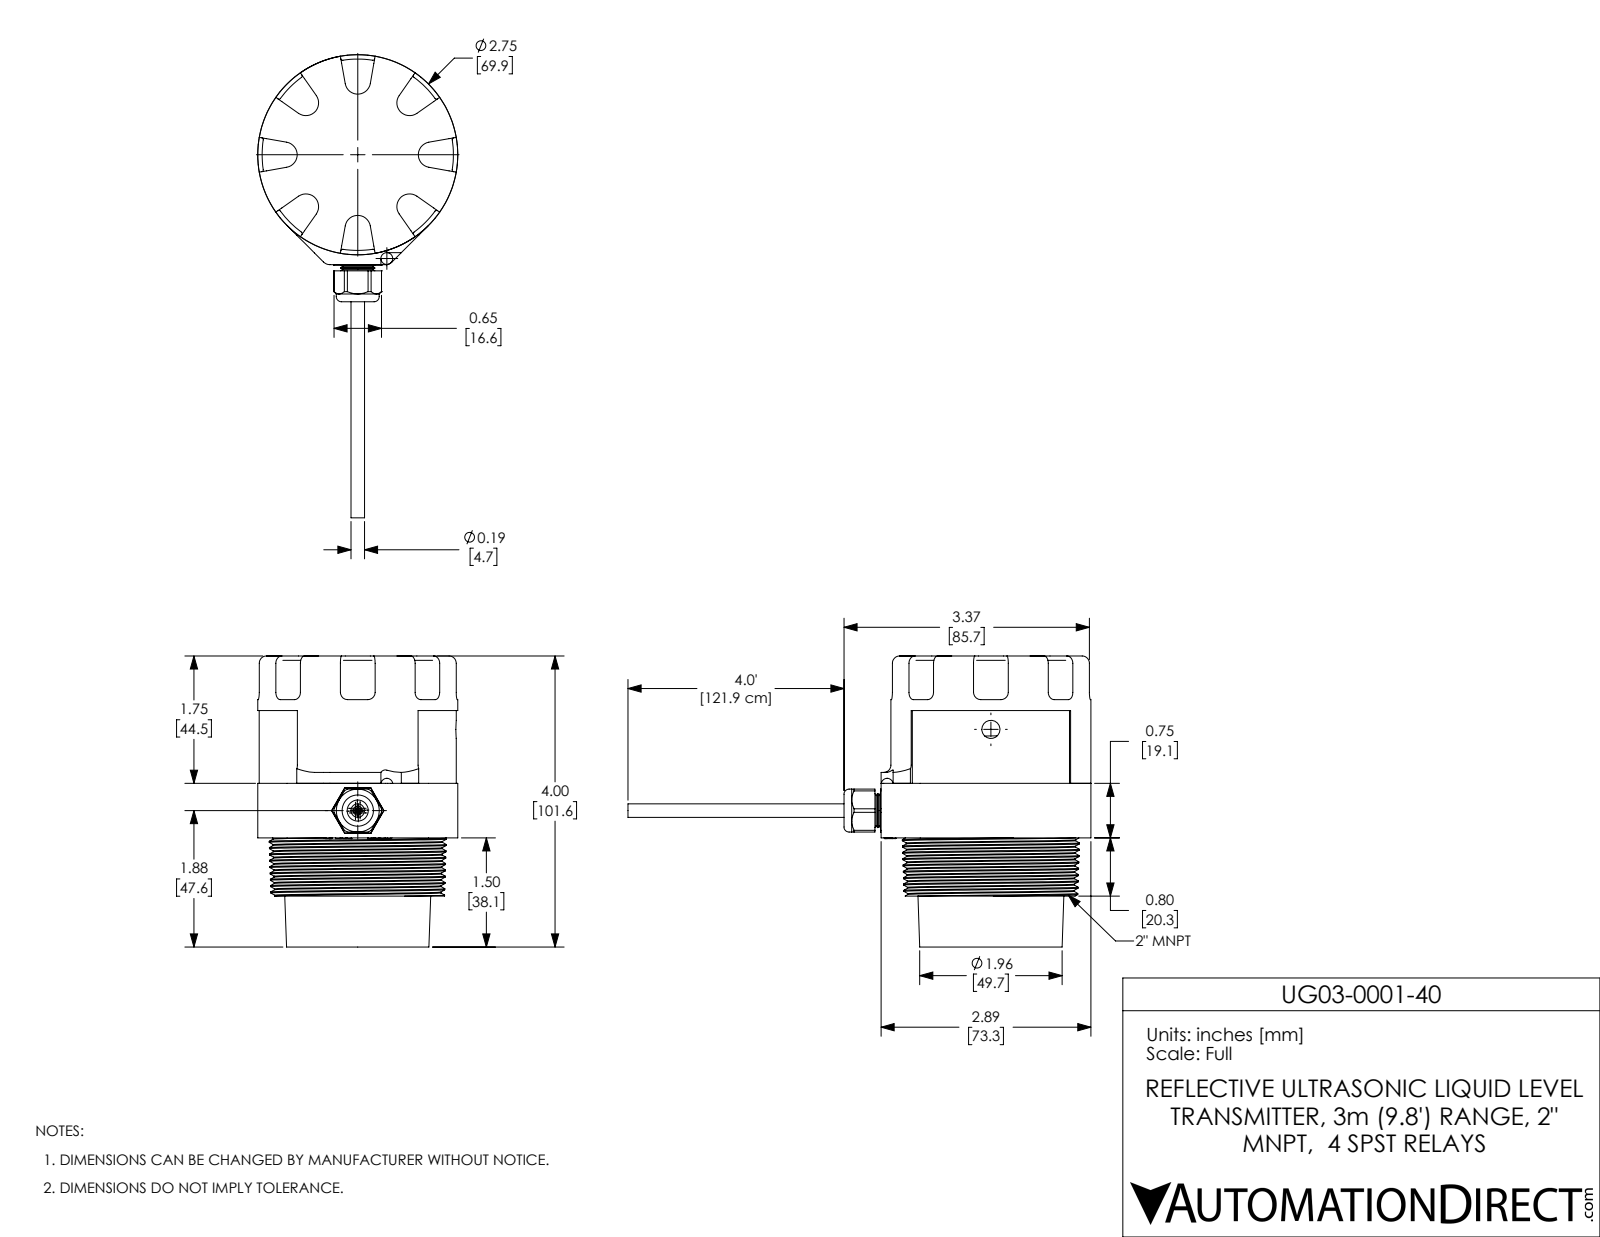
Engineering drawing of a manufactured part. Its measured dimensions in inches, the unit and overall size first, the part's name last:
Units: inches
Overall size (bounding box): 4.969 × 4.969 × 4
Round holes (diameter × count): ⌀0.086 ×1, ⌀0.126 ×1, ⌀0.25 ×1, ⌀0.29 ×1, ⌀0.431 ×1, ⌀1.9 ×1, ⌀2.244 ×1, ⌀2.347 ×1, ⌀2.588 ×1
Round bosses / shafts (diameter × count): ⌀0.045 ×4, ⌀2.75 ×1, ⌀2.362 ×1, ⌀2.231 ×1, ⌀1.725 ×1, ⌀1.665 ×1, ⌀0.59 ×1, ⌀0.186 ×1
Partial cylindrical surfaces — rounded edges, fillets, slot ends (radius × count): R0.025 ×32, R0.1 ×16, R0.175 ×8, R0.125 ×2, R0.082 ×1, R0.327 ×1, R0.902 ×1, R1.315 ×1
Main face-to-face distances: 0.25, 1.75, 1.5, 0.75, 2.5, 2.25, 0.035, 0.035, 1.25, 0.5
Hole centre spacings: 1.481
Volume: 8.666 in³ · Surface area: 126.9 in²
Bodies: 11 solids, 772 faces (253 planar, 167 cylindrical, 352 other)
Part name (STEP PRODUCT): UG01 reduced b1
STEP written by: SolidWorks 2017 (AUTOMOTIVE_DESIGN)
